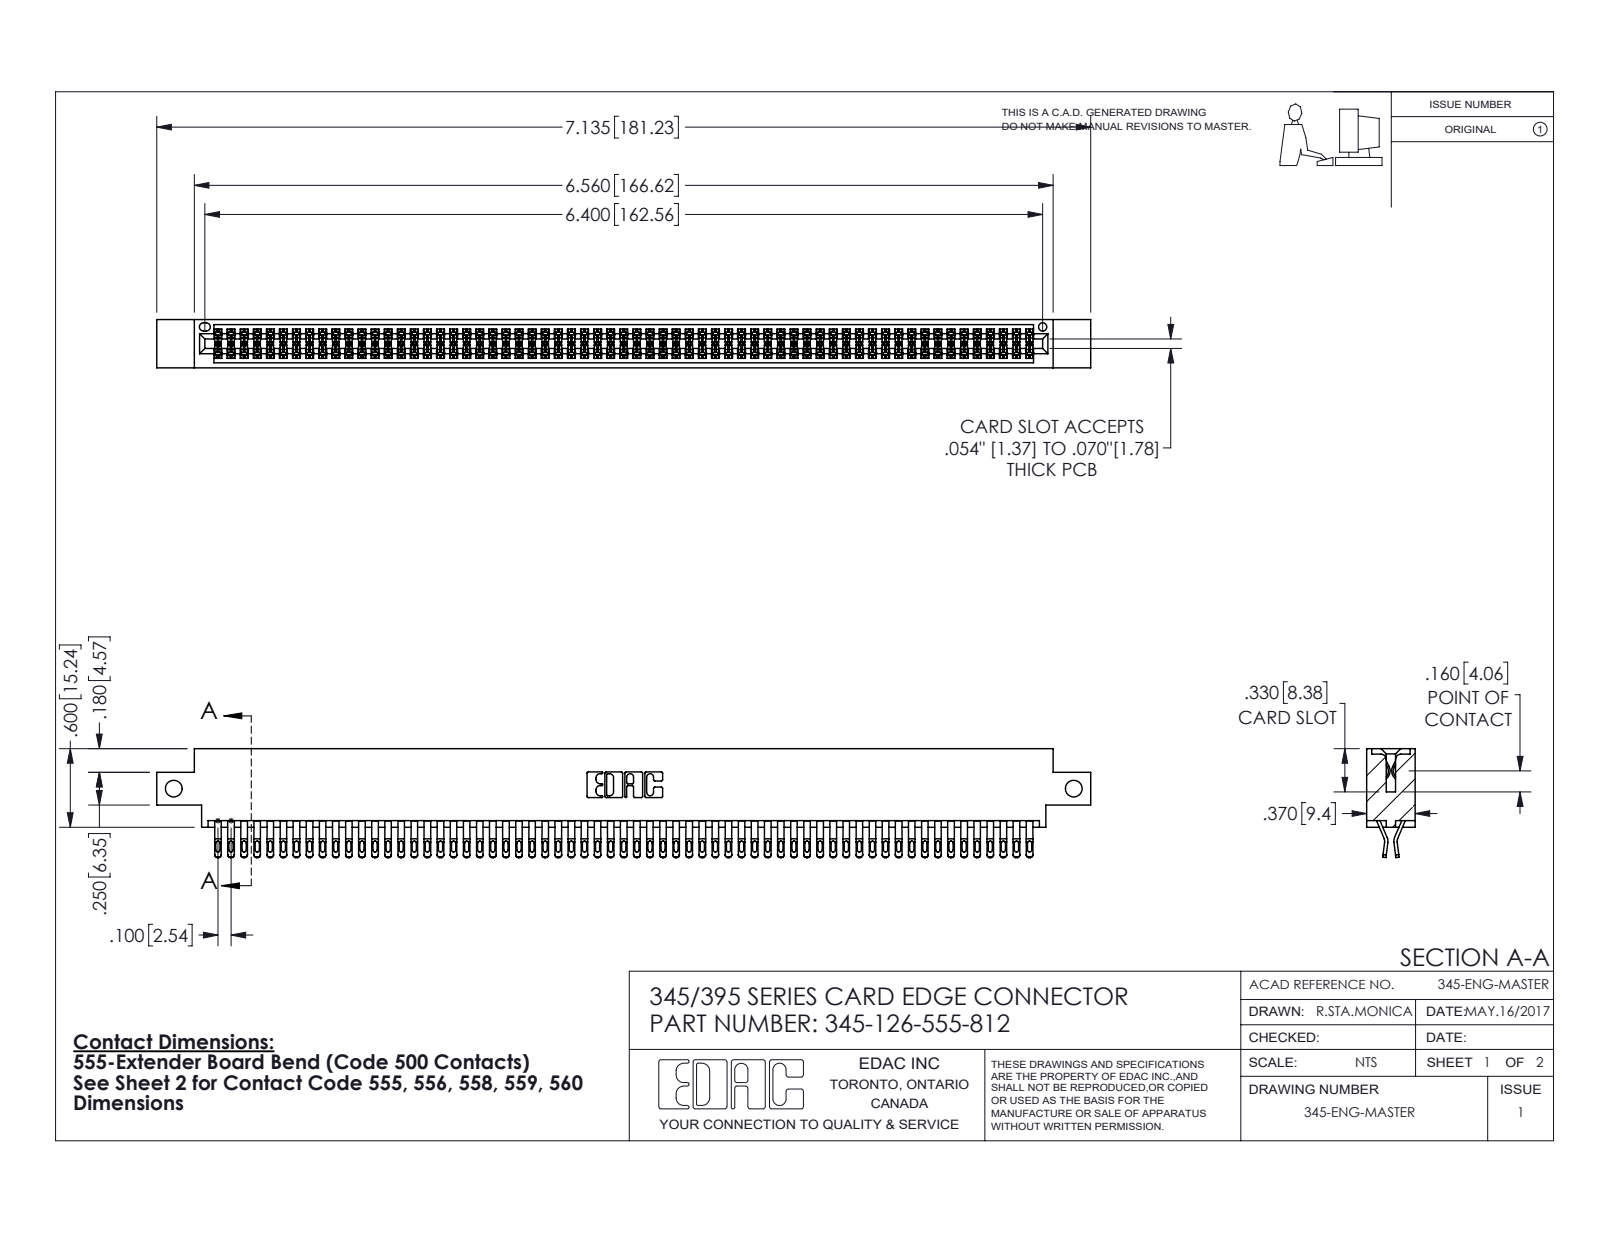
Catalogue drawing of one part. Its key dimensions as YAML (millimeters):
part_name: "345 Part_0.170 Offset - Side Mount; 345-126-555-812; 345-292-001_555 Tail"
step_written_by: "SolidWorks 2016 (CONFIG_CONTROL_DESIGN)"
units: millimeters
bodies: {solids: 127, faces: 7186, planar: 3990, cylindrical: 3196, other: 0}
overall_size: [181.2, 21.1, 9.4]
volume: 17960
surface_area: 28240
round_holes:
  - {diameter: 3.3, count: 2}
  - {diameter: 1.6, count: 1}
partial_cylinders:
  - {radius: 0.4, count: 315}
  - {radius: 0.5, count: 252}
  - {radius: 0.2, count: 189}
  - {radius: 0.3, count: 22}
  - {radius: 0.2, count: 6}
  - {radius: 0.8, count: 6}
  - {radius: 0.7, count: 3}
  - {radius: 0.3, count: 2}
face_to_face_distances: [7.6, 1.8, 9.4, 0.6, 5.1, 2.5, 6.9, 5.7, 4.4, 3.8]
hole_center_spacings: [174.6]
